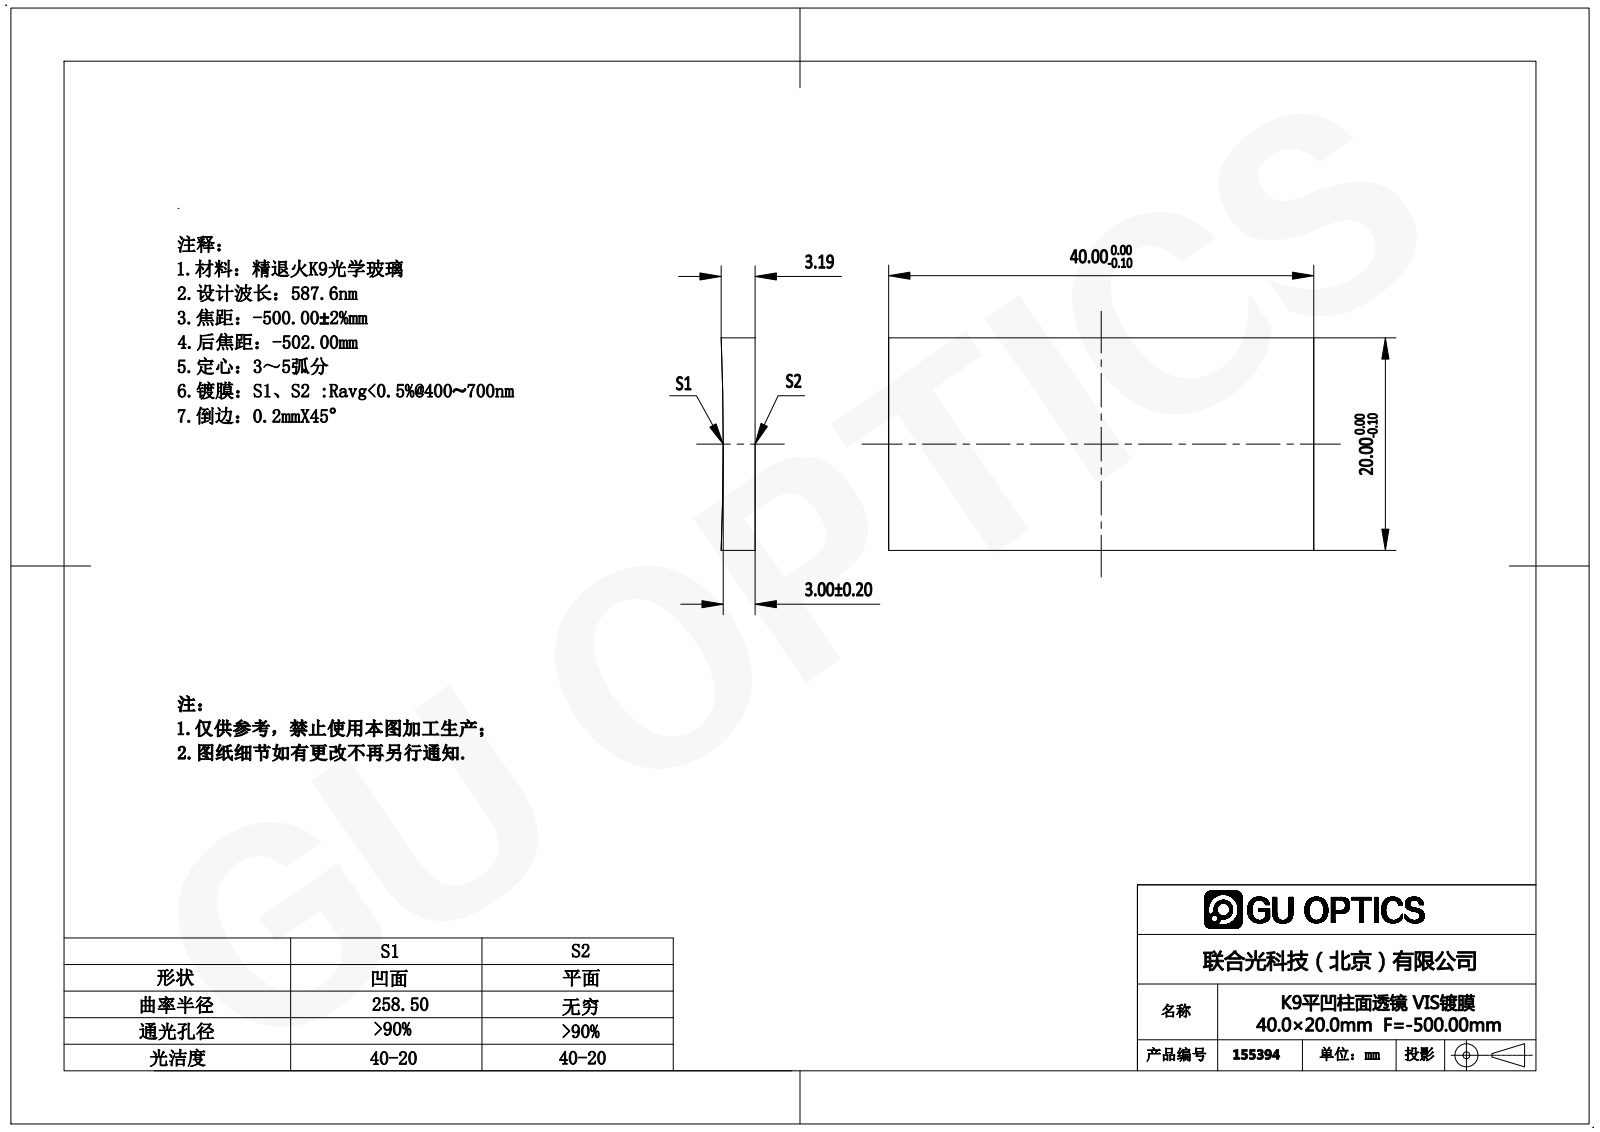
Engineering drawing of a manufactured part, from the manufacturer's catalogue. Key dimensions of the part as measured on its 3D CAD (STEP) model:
Part name (STEP PRODUCT): 155361
STEP written by: SolidWorks 2016 (AUTOMOTIVE_DESIGN)
Units: millimetres
Bodies: 1 solid, 6 faces (5 planar, 1 cylindrical, 0 other)
Overall size (bounding box): 40 × 20 × 3.19
Volume: 2 452 mm³ · Surface area: 1 978 mm²
Partial cylindrical surfaces — rounded edges, fillets, slot ends (radius × count): R258.5 ×1
Main face-to-face distances: 20, 40
